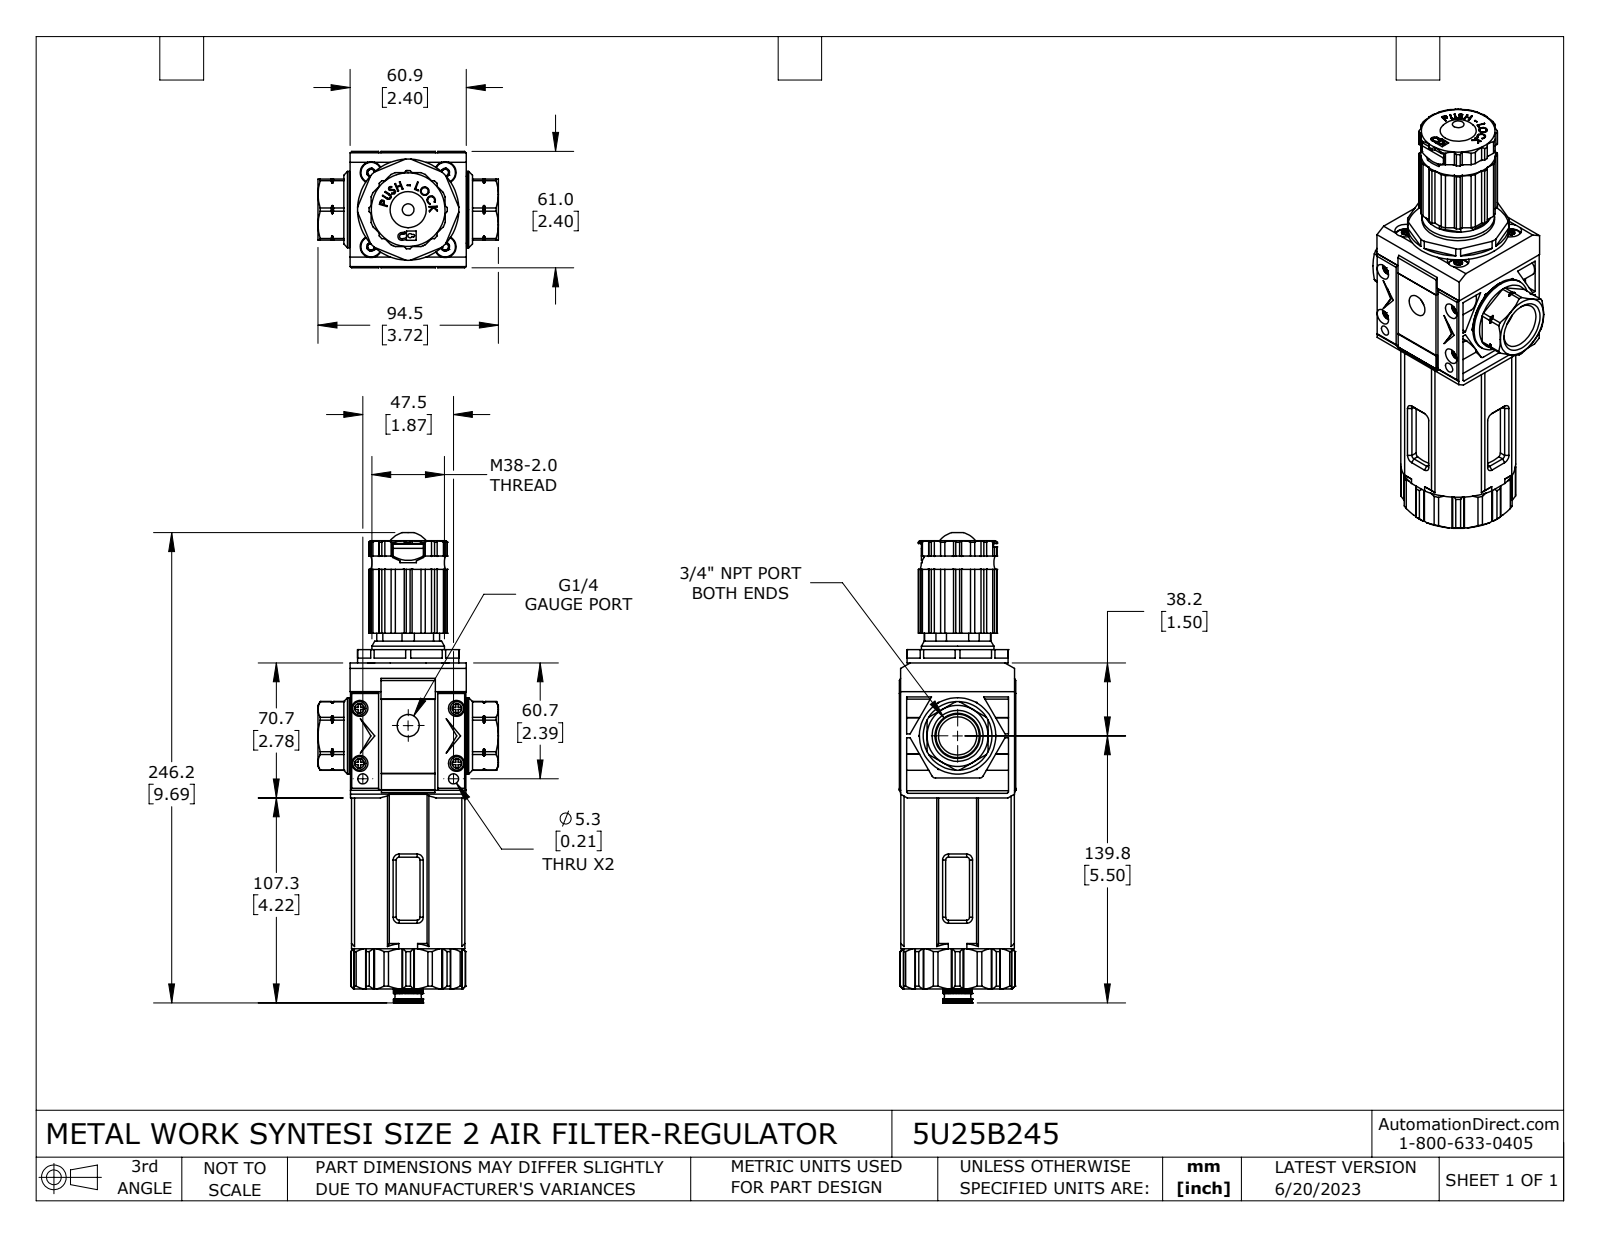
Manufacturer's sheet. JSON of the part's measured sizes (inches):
{"part_name": "5U25B245", "step_written_by": "SolidWorks 2021 (CONFIG_CONTROL_DESIGN)", "units": "inches", "bodies": {"solids": 15, "faces": 2047, "planar": 1264, "cylindrical": 503, "other": 280}, "overall_size": [9.693, 3.72, 2.402], "volume_in3": 29.06, "surface_area_in2": 223.3, "round_holes": [[0.128, 4], [0.165, 4], [0.331, 4], [0.449, 4], [0.209, 2], [0.126, 1], [0.276, 1], [0.343, 1], [0.457, 1], [0.787, 1], [1.25, 1], [1.411, 1]], "round_bosses_or_shafts": [[0.276, 4], [0.189, 4], [0.15, 4], [2.087, 1], [1.575, 1], [1.496, 1], [1.378, 1], [1.248, 1]], "partial_cylinders_radius": [[0.011, 28], [0.02, 16], [0.059, 8], [0.069, 4], [0.191, 4], [0.807, 4], [0.008, 2], [0.079, 2]], "face_to_face_distances": [5.303, 2.39, 3.11, 3.205, 2.098, 1.13, 0.591, 2.193, 1.799, 2.402], "hole_center_spacings": [1.08, 1.528, 0.325, 1.057, 1.134, 1.265, 1.443, 1.454]}
